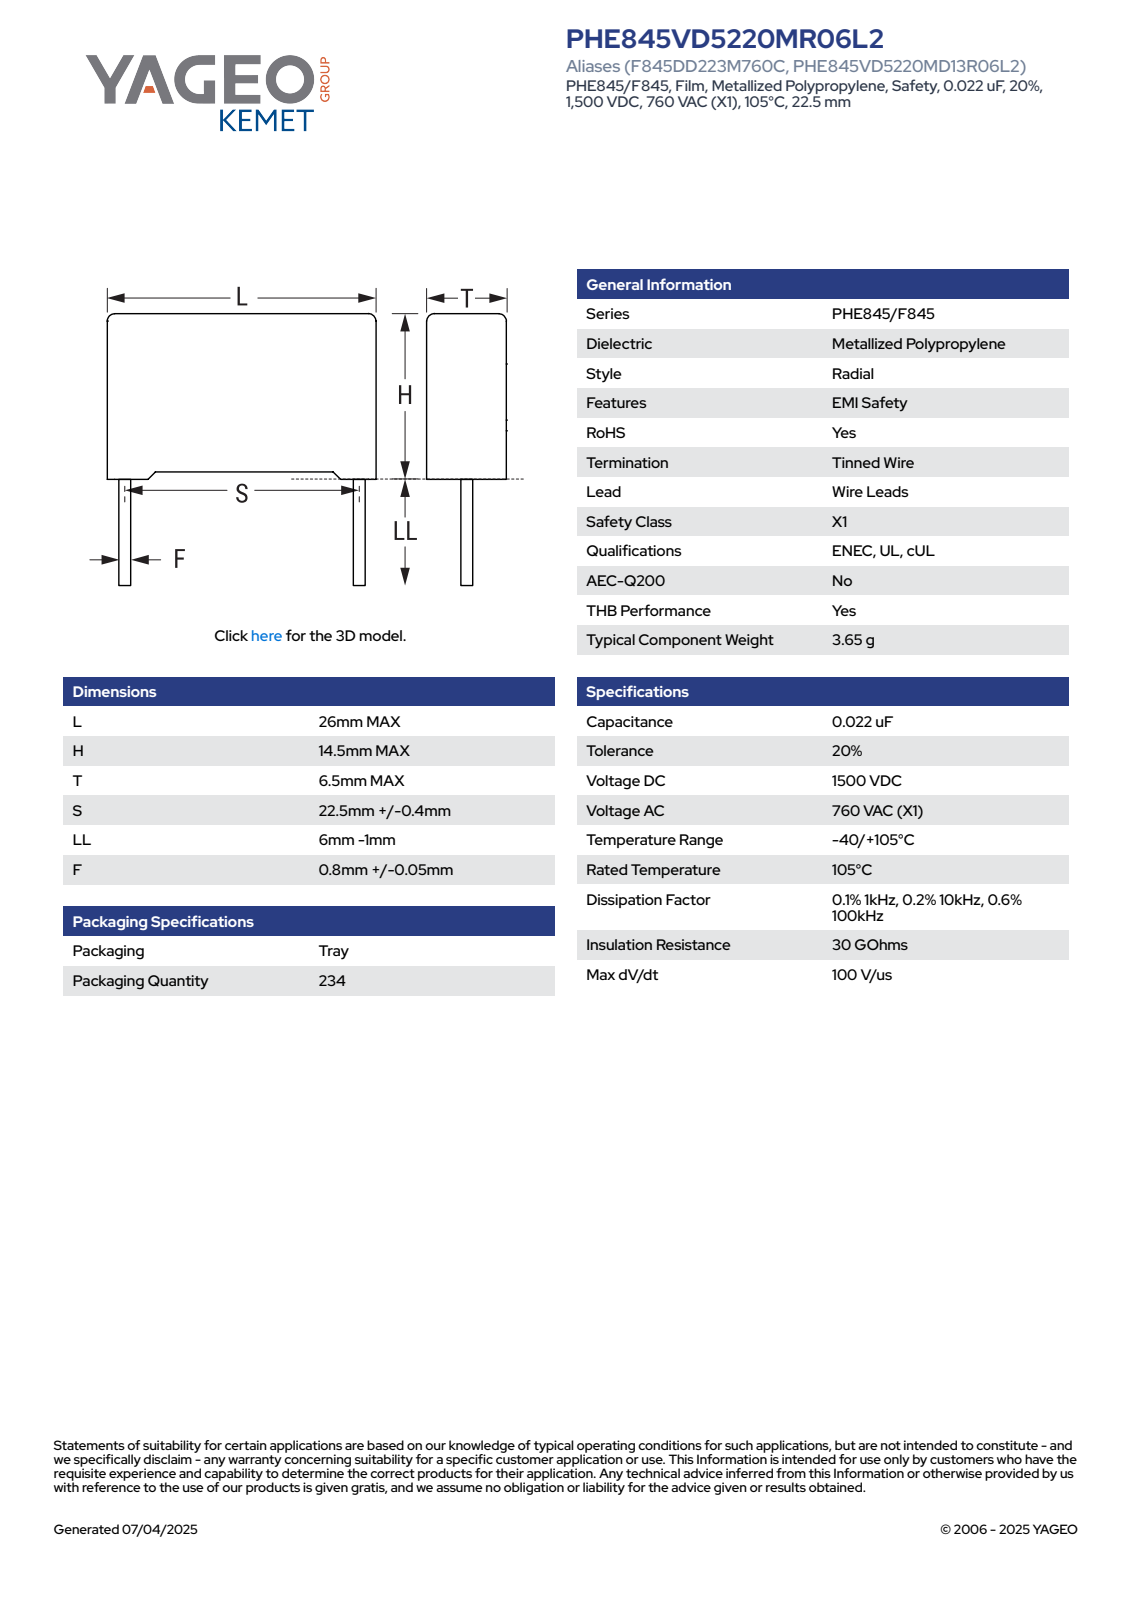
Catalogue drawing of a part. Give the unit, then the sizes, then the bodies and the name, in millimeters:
Units: millimetres
Overall size (bounding box): 26 × 19.5 × 6.5
Round bosses / shafts (diameter × count): ⌀0.85 ×2
Partial cylindrical surfaces — rounded edges, fillets, slot ends (radius × count): R0.5 ×4
Main face-to-face distances: 6.5, 13.75, 26, 14, 0.87, 0.5, 0.75, 14.5, 5.63, 4.76
Volume: 2 351 mm³ · Surface area: 1 354 mm²
Bodies: 4 solids, 85 faces (77 planar, 8 cylindrical, 0 other)
Part name (STEP PRODUCT): CFR_RB2_26X14.5X6.5_L26H14.5T6.5S22.5LL5F0.85
STEP written by: SolidWorks 2021 (AUTOMOTIVE_DESIGN)
